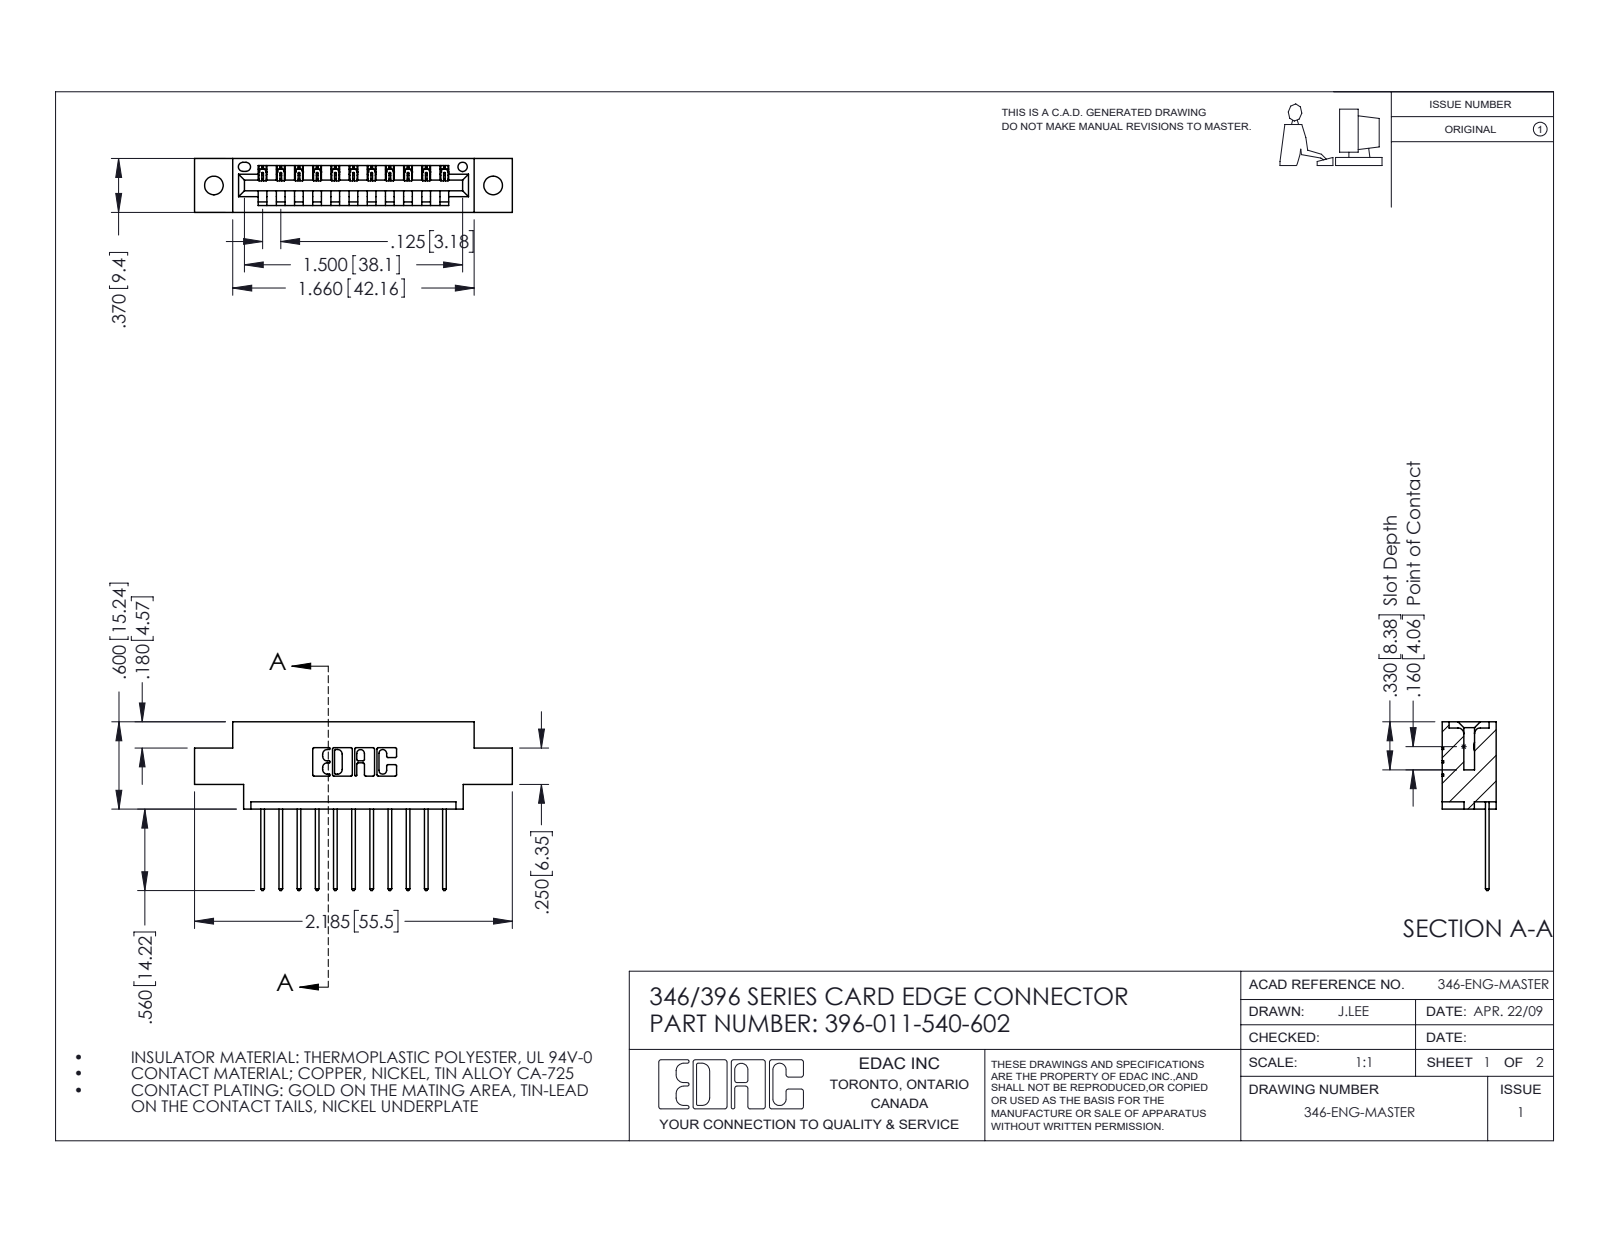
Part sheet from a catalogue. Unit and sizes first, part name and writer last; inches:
Units: inches
Overall size (bounding box): 2.185 × 1.16 × 0.37
Round holes (diameter × count): ⌀0.128 ×2, ⌀0.064 ×1
Partial cylindrical surfaces — rounded edges, fillets, slot ends (radius × count): R0.006 ×22, R0.01 ×22, R0.01 ×22, R0.007 ×6, R0.031 ×6, R0.026 ×3, R0.031 ×2, R0.04 ×2
Main face-to-face distances: 0.25, 0.37, 0.048, 0.322, 0.072, 0.298, 0.025, 0.148, 0.222, 0.1
Hole centre spacings: 0.246, 1.715, 1.92
Volume: 0.3 in³ · Surface area: 9.015 in²
Bodies: 12 solids, 764 faces (520 planar, 244 cylindrical, 0 other)
Part name (STEP PRODUCT): 346 Part_0.170 Offset - 0.128 Dia; 345-292-001_345-293-140; 396-011-540-602
STEP written by: SolidWorks 2016 (CONFIG_CONTROL_DESIGN)
